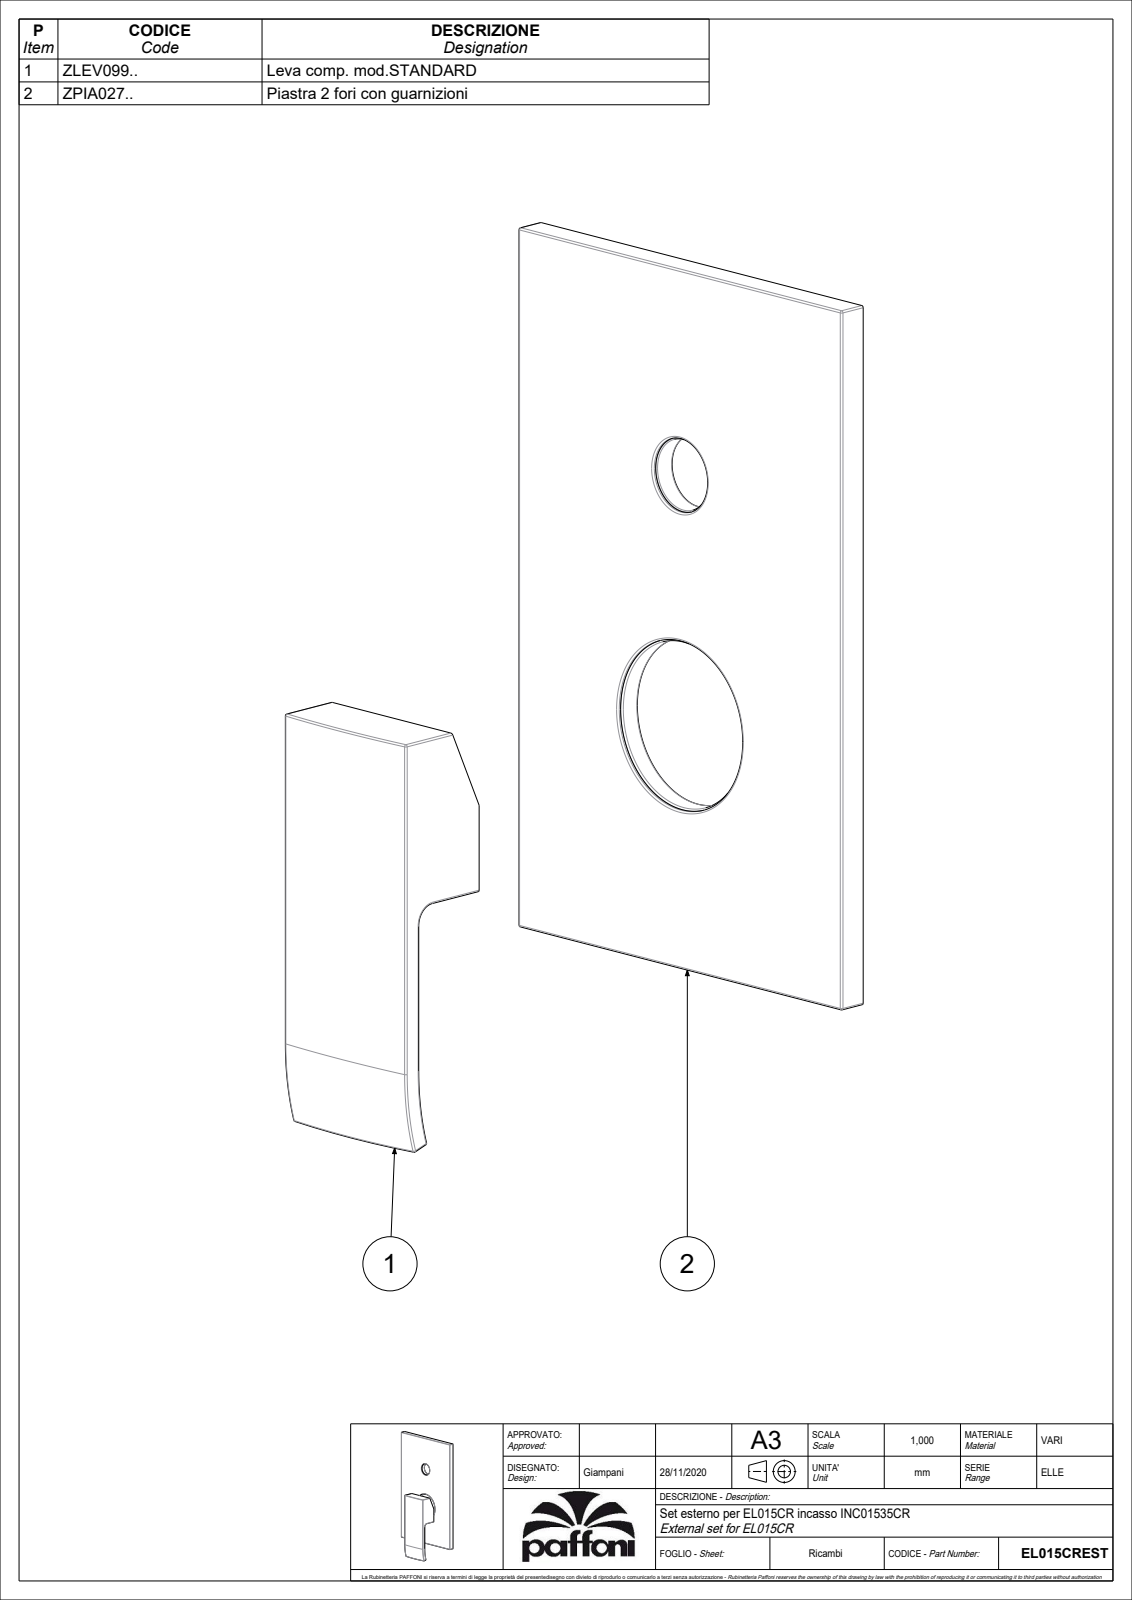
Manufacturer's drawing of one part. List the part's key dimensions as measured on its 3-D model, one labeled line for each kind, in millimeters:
Part name (STEP PRODUCT): EL015CREST
STEP written by: CREO PARAMETRIC BY PTC INC, 2020044 (CONFIG_CONTROL_DESIGN)
Units: millimetres
Bodies: 2 solids, 229 faces (77 planar, 85 cylindrical, 67 other)
Overall size (bounding box): 212.38 × 120 × 38
Volume: 146 609 mm³ · Surface area: 74 349 mm²
Round holes (diameter × count): ⌀3 ×1, ⌀3.3 ×1, ⌀5.5 ×1, ⌀7.8 ×1, ⌀19.2 ×1, ⌀20 ×1, ⌀23.2 ×1, ⌀45 ×1, ⌀46 ×1
Round bosses / shafts (diameter × count): ⌀51 ×1, ⌀49 ×1, ⌀25 ×1, ⌀23 ×1, ⌀7.6 ×1, ⌀5 ×1
Partial cylindrical surfaces — rounded edges, fillets, slot ends (radius × count): R0.5 ×18, R1.5 ×14, R1 ×8, R2 ×4, R300 ×2, R2.25 ×1
Main face-to-face distances: 7.5, 2.5, 5, 0.5, 37.5, 82.5, 22.5, 45, 15, 97.5
Hole centre spacings: 68
